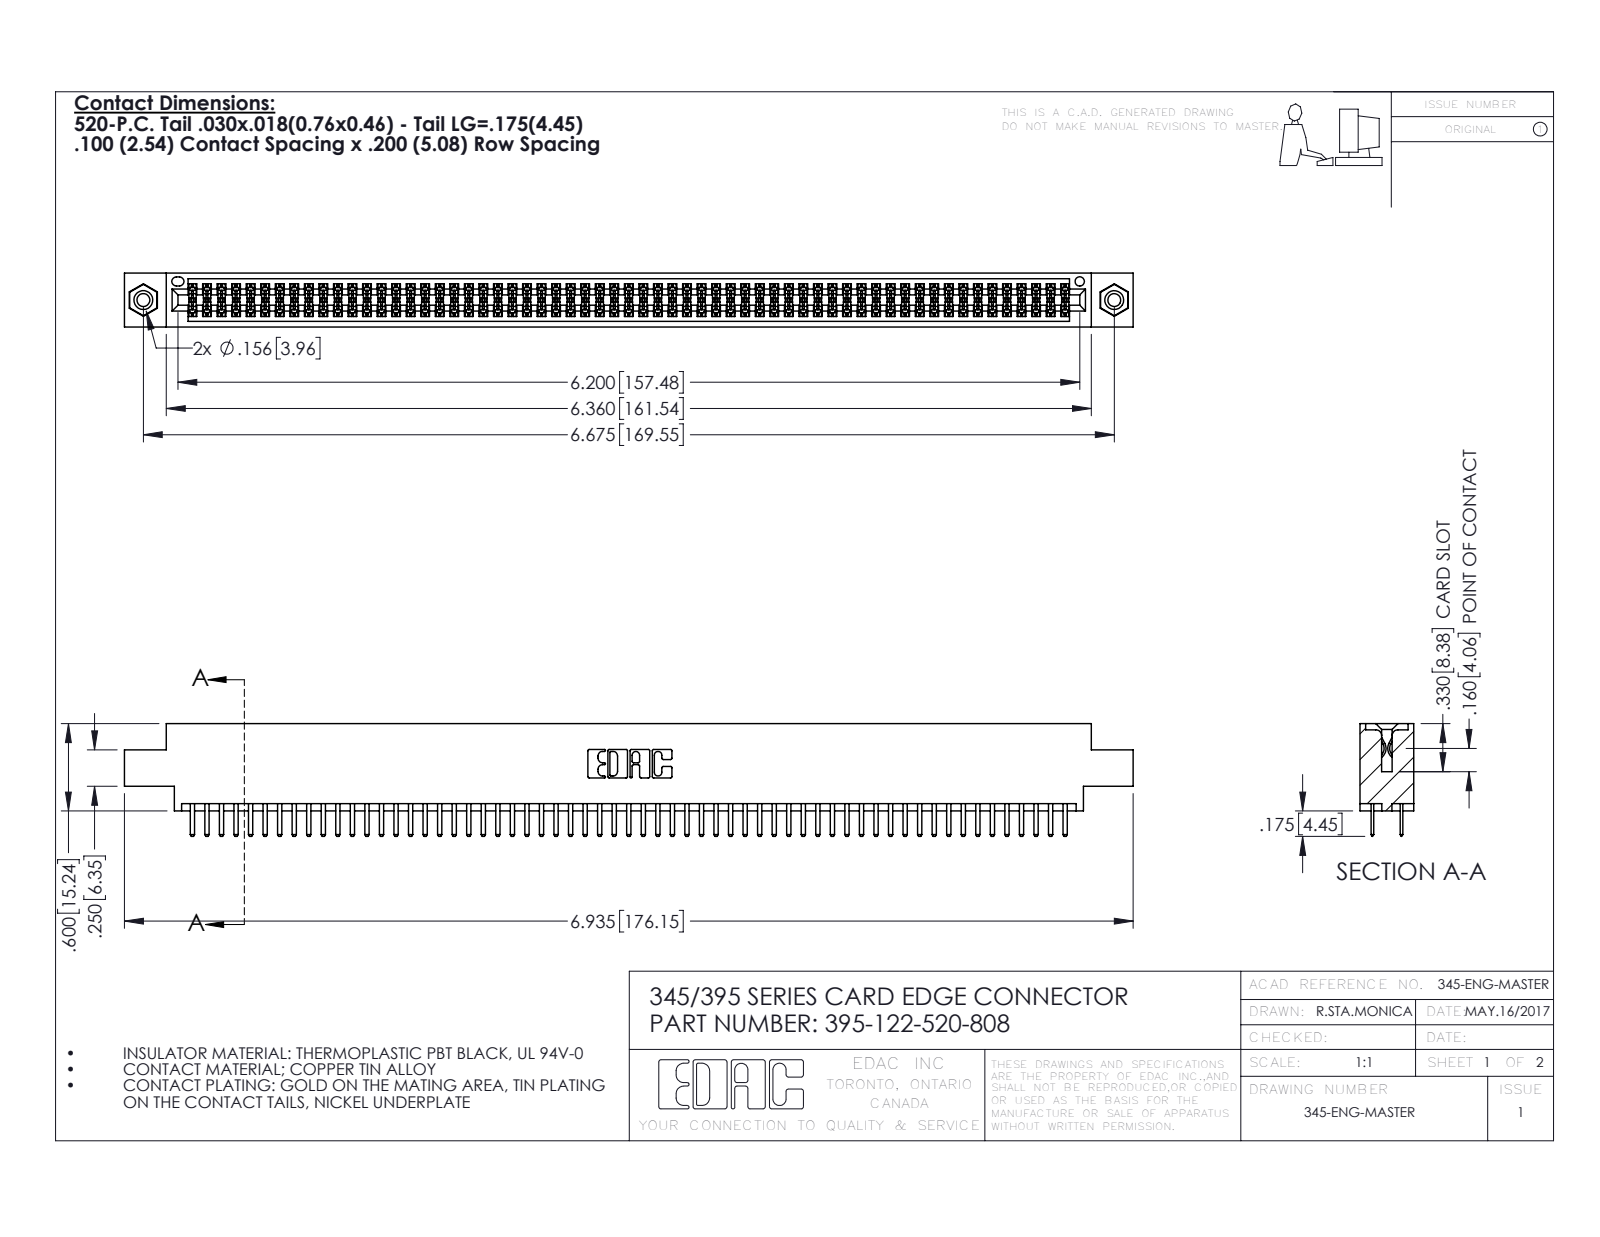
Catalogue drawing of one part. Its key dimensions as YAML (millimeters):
part_name: "345 Part_0.170 Offset - 0.156 Dia-TI; 345-292-001_345-293-120; 345-250-001_345-250-003-102; 395-122-520-808"
step_written_by: "SolidWorks 2016 (CONFIG_CONTROL_DESIGN)"
units: millimeters
bodies: {solids: 125, faces: 6778, planar: 4386, cylindrical: 2376, other: 16}
overall_size: [176.1, 19.7, 9.4]
volume: 17110
surface_area: 25710
round_holes:
  - {diameter: 2.3, count: 2}
  - {diameter: 3.2, count: 2}
  - {diameter: 4, count: 2}
  - {diameter: 1.6, count: 1}
round_bosses_or_shafts:
  - {diameter: 3.9, count: 2}
partial_cylinders:
  - {radius: 0.2, count: 183}
  - {radius: 0.3, count: 126}
  - {radius: 0.3, count: 22}
  - {radius: 0.2, count: 6}
  - {radius: 0.8, count: 6}
  - {radius: 0.7, count: 3}
  - {radius: 0.4, count: 2}
  - {radius: 0.5, count: 2}
face_to_face_distances: [1.8, 7.6, 5.1, 9.4, 2.5, 6.9, 0.6, 5.7, 0.6, 1.8]
hole_center_spacings: [6.9, 163.6, 169.5]
